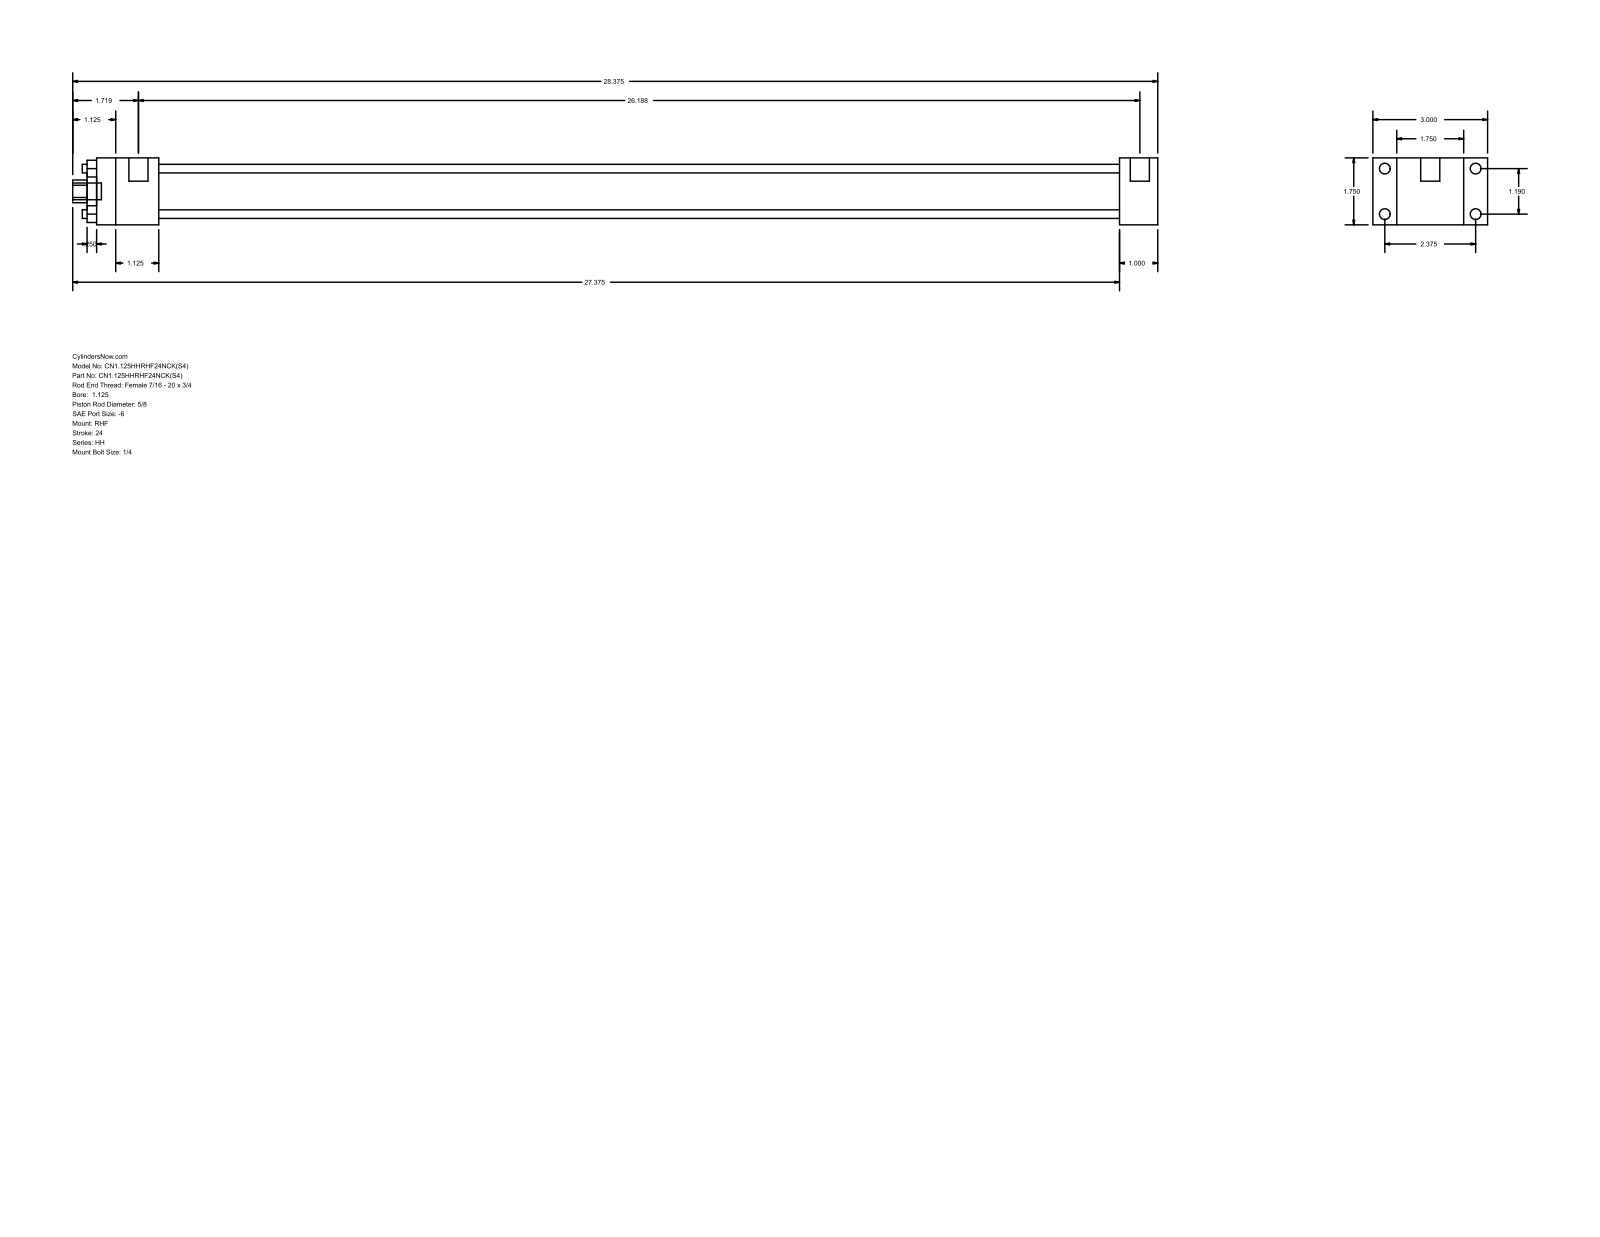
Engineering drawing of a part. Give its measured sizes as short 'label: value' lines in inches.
name: HH_RHF__0112_0.625
written by: GSSL Pune (CONFIG_CONTROL_DESIGN)
unit: in
bodies: 0 solids, 88 faces (60 planar, 28 cylindrical, 0 other)
size: 28.375 × 3 × 1.75
holes: 4× ⌀0.225, 1× ⌀0.625, 1× ⌀1.125, 1× ⌀1.375
bosses: 4× ⌀0.281, 4× ⌀0.219, 2× ⌀0.5, 1× ⌀0.437
rounds: 1× R0.297
face distances: 1.75, 0.625, 2.375, 1, 3, 25.125, 26.125, 1.625, 26.75, 27.75
hole spacings: 0.841, 1.19, 1.683
